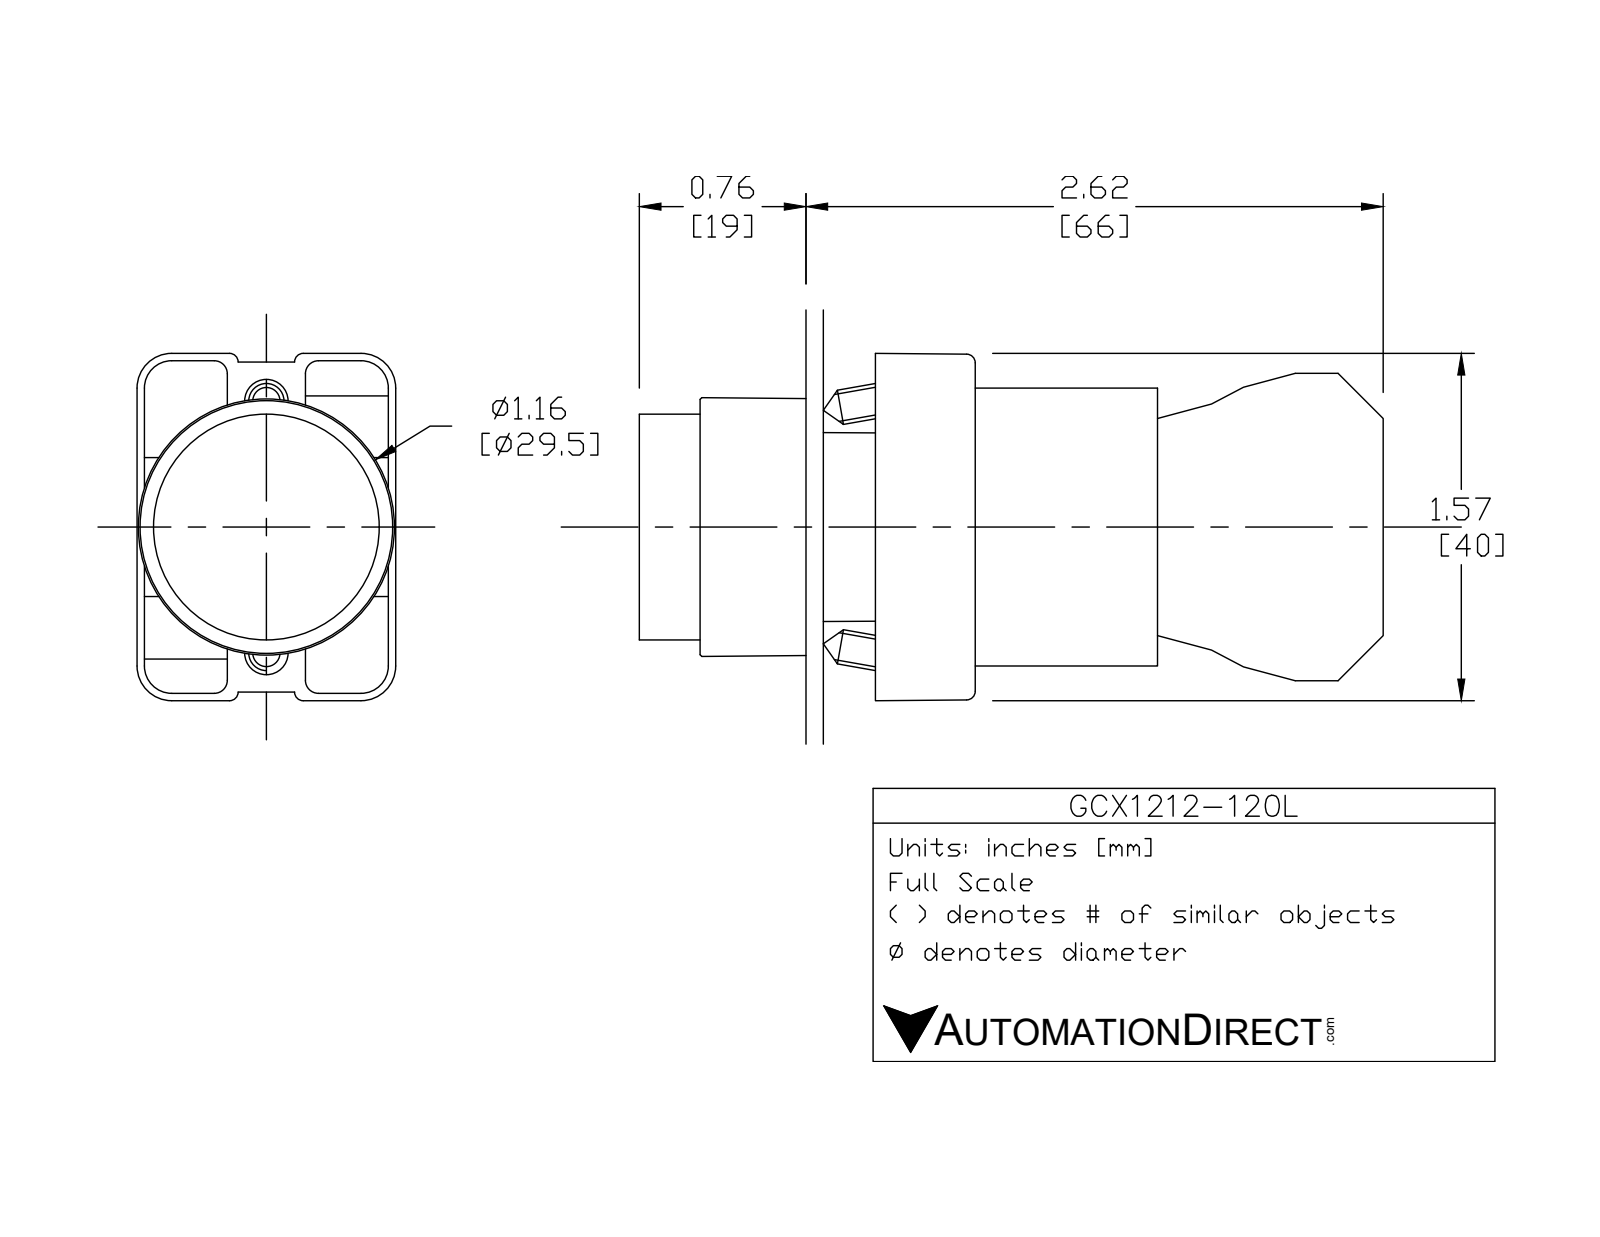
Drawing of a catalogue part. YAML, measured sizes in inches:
part_name: "ecx1029; ecx1040; GCX1212L OPERATOR; ECX1050 (+1 more)"
step_written_by: "SolidWorks 2016 (AUTOMOTIVE_DESIGN)"
units: inches
bodies: {solids: 7, faces: 425, planar: 250, cylindrical: 144, other: 31}
overall_size: [3.319, 1.581, 1.177]
volume: 2.721
surface_area: 36.32
round_holes:
  - {diameter: 0.079, count: 2}
  - {diameter: 0.124, count: 2}
  - {diameter: 0.13, count: 2}
  - {diameter: 0.087, count: 1}
  - {diameter: 0.197, count: 1}
  - {diameter: 0.469, count: 1}
  - {diameter: 0.878, count: 1}
  - {diameter: 0.888, count: 1}
  - {diameter: 1.024, count: 1}
round_bosses_or_shafts:
  - {diameter: 0.157, count: 4}
  - {diameter: 1.175, count: 1}
  - {diameter: 1.004, count: 1}
  - {diameter: 0.945, count: 1}
  - {diameter: 0.856, count: 1}
  - {diameter: 0.78, count: 1}
  - {diameter: 0.504, count: 1}
partial_cylinders:
  - {radius: 0.059, count: 24}
  - {radius: 0.041, count: 12}
  - {radius: 0.124, count: 12}
  - {radius: 0.157, count: 12}
  - {radius: 0.039, count: 8}
  - {radius: 0.128, count: 2}
  - {radius: 0.02, count: 1}
  - {radius: 0.063, count: 1}
face_to_face_distances: [0.827, 0.579, 1.171, 2.02, 1.193, 0.031, 0.033, 0.573, 1.165, 0.593]
hole_center_spacings: [0.236, 0.544, 0.472, 0.49]
